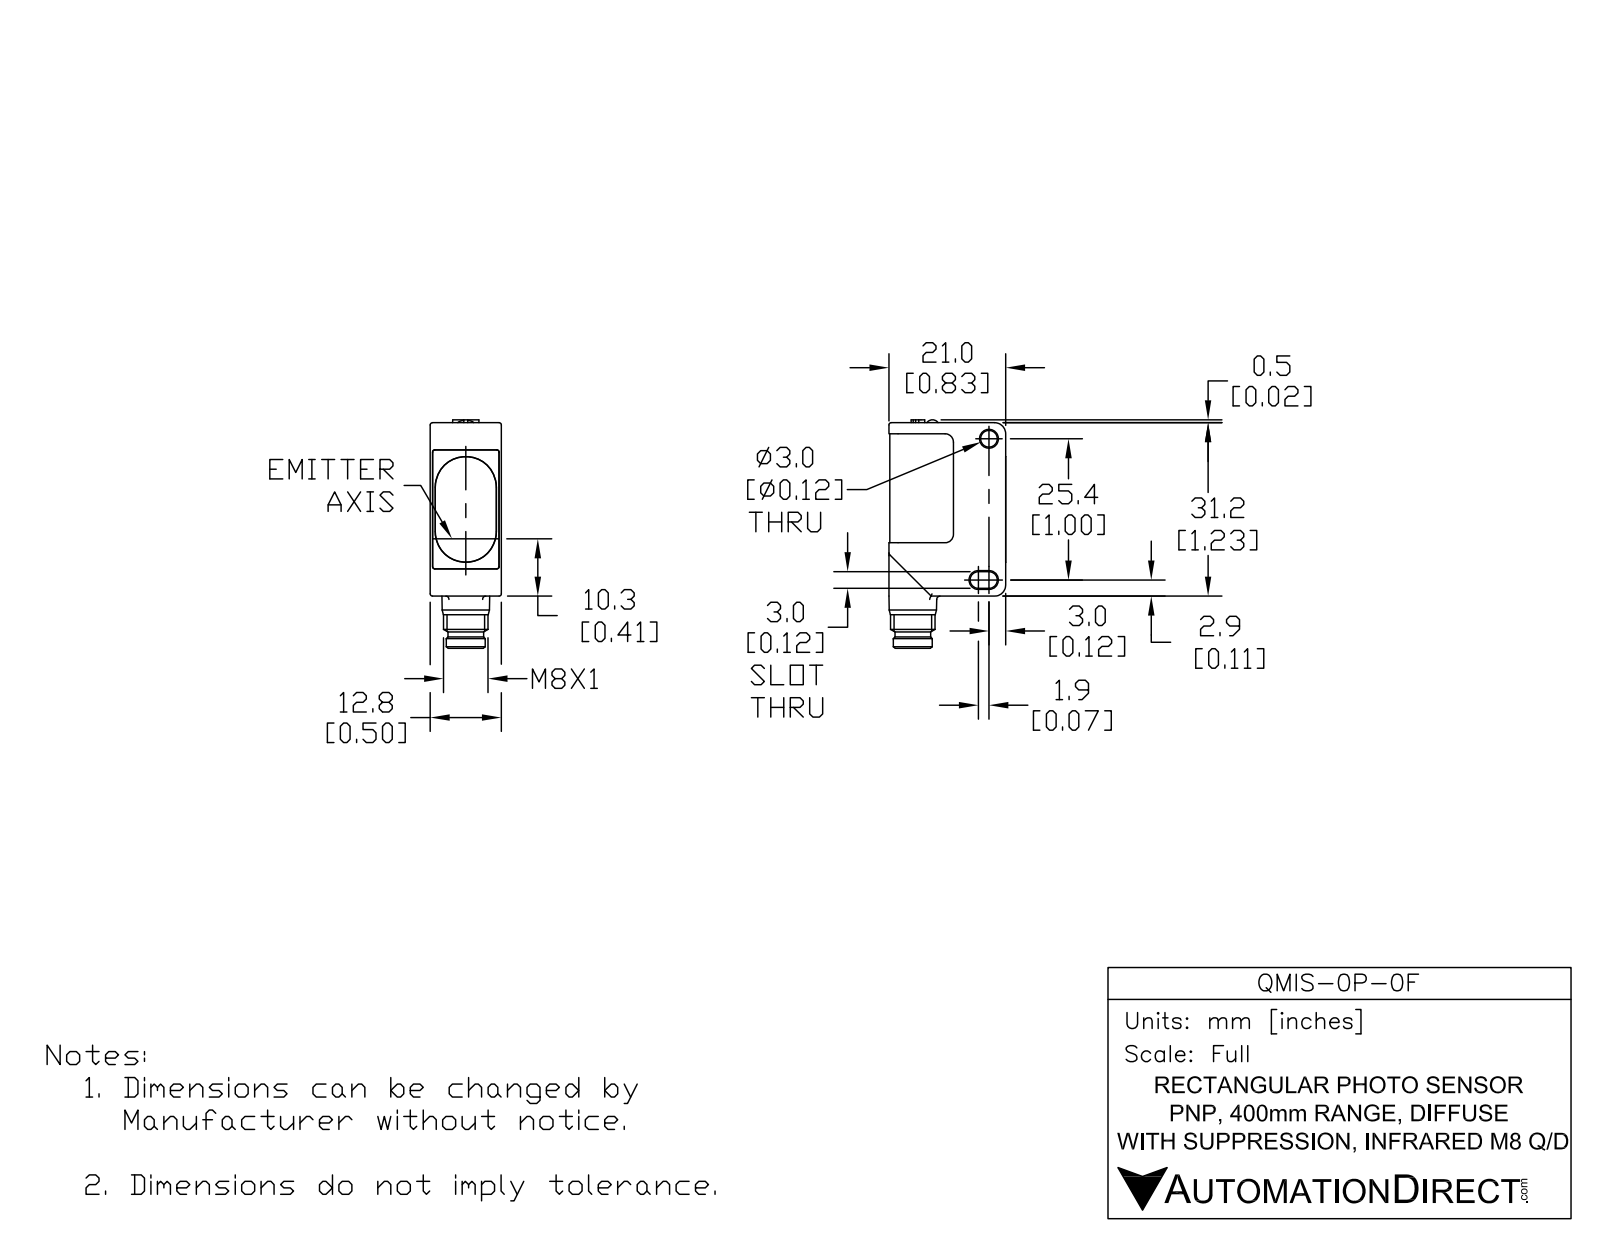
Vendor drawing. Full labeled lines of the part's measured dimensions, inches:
Part name (STEP PRODUCT): QMIS-0P-0F
STEP written by: SolidWorks 2017 (AUTOMOTIVE_DESIGN)
Units: inches
Bodies: 7 solids, 262 faces (123 planar, 92 cylindrical, 47 other)
Overall size (bounding box): 1.618 × 0.827 × 0.504
Volume: 0.468 in³ · Surface area: 7.721 in²
Round holes (diameter × count): ⌀0.118 ×1, ⌀0.173 ×1, ⌀0.228 ×1
Round bosses / shafts (diameter × count): ⌀0.039 ×4, ⌀0.315 ×1, ⌀0.276 ×1, ⌀0.252 ×1, ⌀0.122 ×1, ⌀0.11 ×1
Partial cylindrical surfaces — rounded edges, fillets, slot ends (radius × count): R0.016 ×10, R0.059 ×7, R0.024 ×4, R0.039 ×4, R0.177 ×4, R0.02 ×3, R0.065 ×2, R0.079 ×2
Main face-to-face distances: 0.498, 0.504, 0.02, 0.11, 0.039, 0.016, 0.071, 0.492, 0.488, 0.482
Hole centre spacings: 0.311
